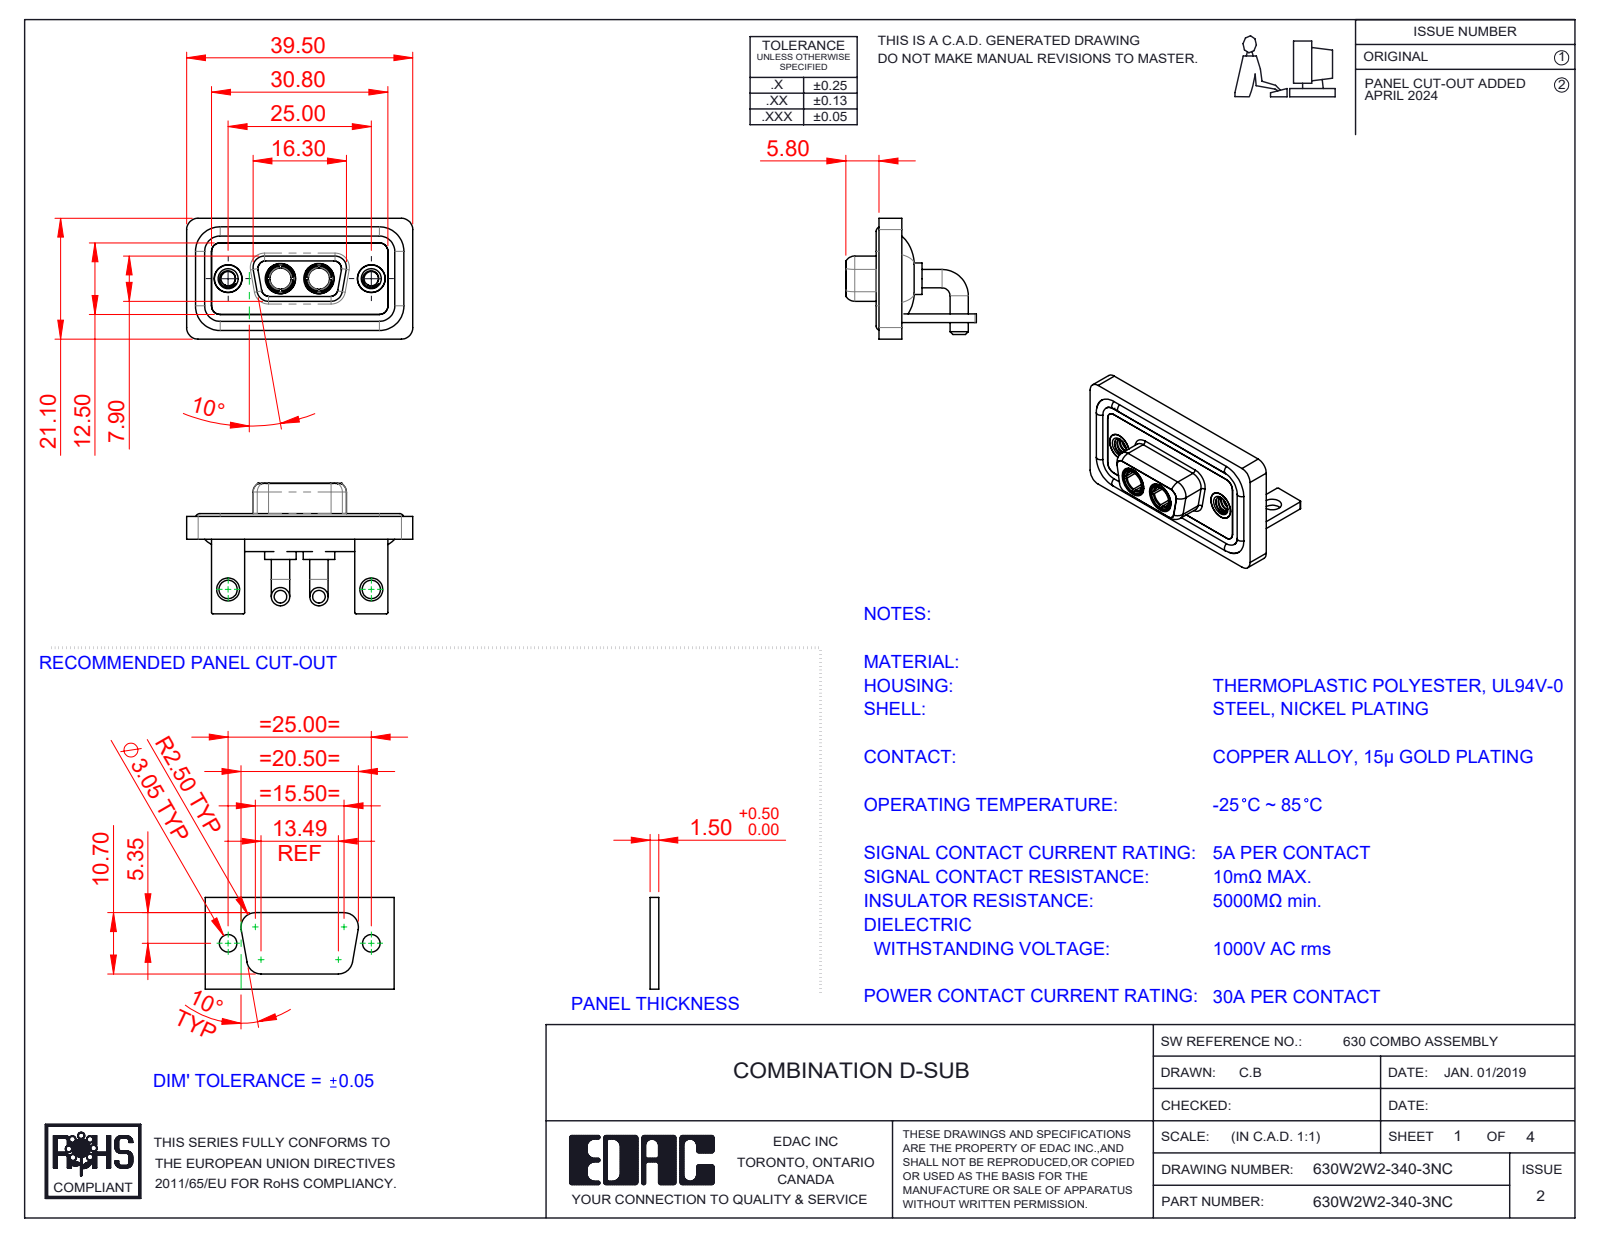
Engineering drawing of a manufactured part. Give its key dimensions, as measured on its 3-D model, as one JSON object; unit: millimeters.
{"part_name": "630Combo Housing_2W2; 630Combo Stabilizer Bracket_50 Contacts; Power Socket_30A RA; 630Combo Threaded Rivet_A (+4 more)", "step_written_by": "SolidWorks 2023 (CONFIG_CONTROL_DESIGN)", "units": "millimeters", "bodies": {"solids": 13, "faces": 584, "planar": 183, "cylindrical": 260, "other": 141}, "overall_size": [39.5, 22.8, 21.1], "volume_mm3": 5231, "surface_area_mm2": 8561, "round_holes": [[4.85, 4], [2.5, 2], [3.2, 2], [3.7, 2], [4, 2], [4.05, 2], [5, 2], [5.3, 2]], "round_bosses_or_shafts": [[3.2, 4], [1.6, 4], [5.5, 2], [5.2, 2], [4.96, 2], [4.95, 2], [4.8, 2], [4.75, 2]], "partial_cylinders_radius": [[2, 19], [1.5, 18], [0.25, 16], [1.35, 8], [1.6, 8], [0.5, 5], [0.6, 4], [0.65, 4]], "face_to_face_distances": [0.4, 2.9, 1.5, 1.8, 1.1, 3.7, 0.8, 2.5, 1.6, 3.1], "hole_center_spacings": [9.14, 15.86, 25, 6.72]}
